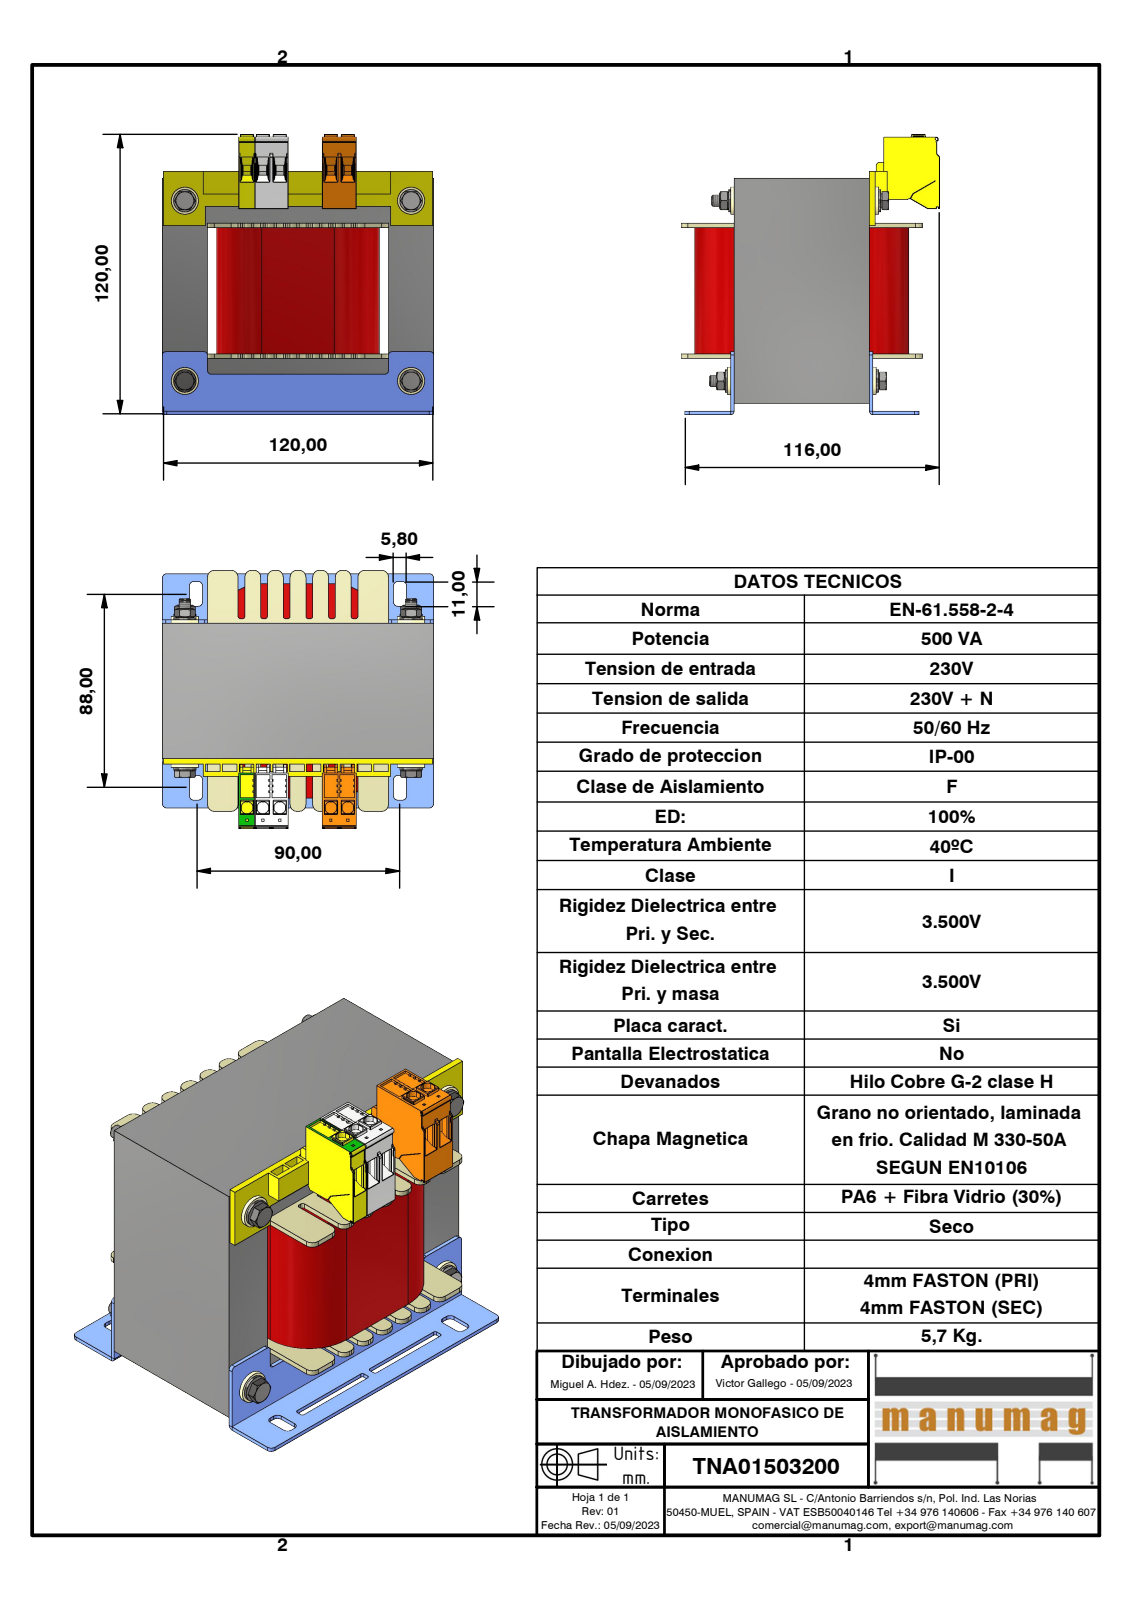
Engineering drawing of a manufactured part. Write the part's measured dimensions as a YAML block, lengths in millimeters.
part_name: "TNA01503200; EI120 x 100 - 60 (Rc40); EI120; centrador M5 (+8 more)"
step_written_by: "Autodesk Inventor 2023 (AUTOMOTIVE_DESIGN)"
units: millimeters
bodies: {solids: 32, faces: 5330, planar: 4334, cylindrical: 692, other: 304}
overall_size: [124.5, 120, 114.65]
volume: 869115
surface_area: 172111
round_holes:
  - {diameter: 4.13, count: 4}
  - {diameter: 5, count: 4}
  - {diameter: 5.3, count: 4}
  - {diameter: 6.6, count: 4}
  - {diameter: 6.8, count: 2}
round_bosses_or_shafts:
  - {diameter: 12, count: 4}
  - {diameter: 10, count: 4}
  - {diameter: 6.7, count: 4}
  - {diameter: 5.9, count: 4}
  - {diameter: 4.57, count: 4}
partial_cylinders:
  - {radius: 0.15, count: 214}
  - {radius: 0.2, count: 58}
  - {radius: 1, count: 28}
  - {radius: 3, count: 28}
  - {radius: 2, count: 20}
  - {radius: 0.8, count: 17}
  - {radius: 0.5, count: 14}
  - {radius: 0.3, count: 6}
face_to_face_distances: [80, 20, 60, 40, 100, 1.5, 16, 56, 4, 24]
hole_center_spacings: [80, 100, 128.06]
